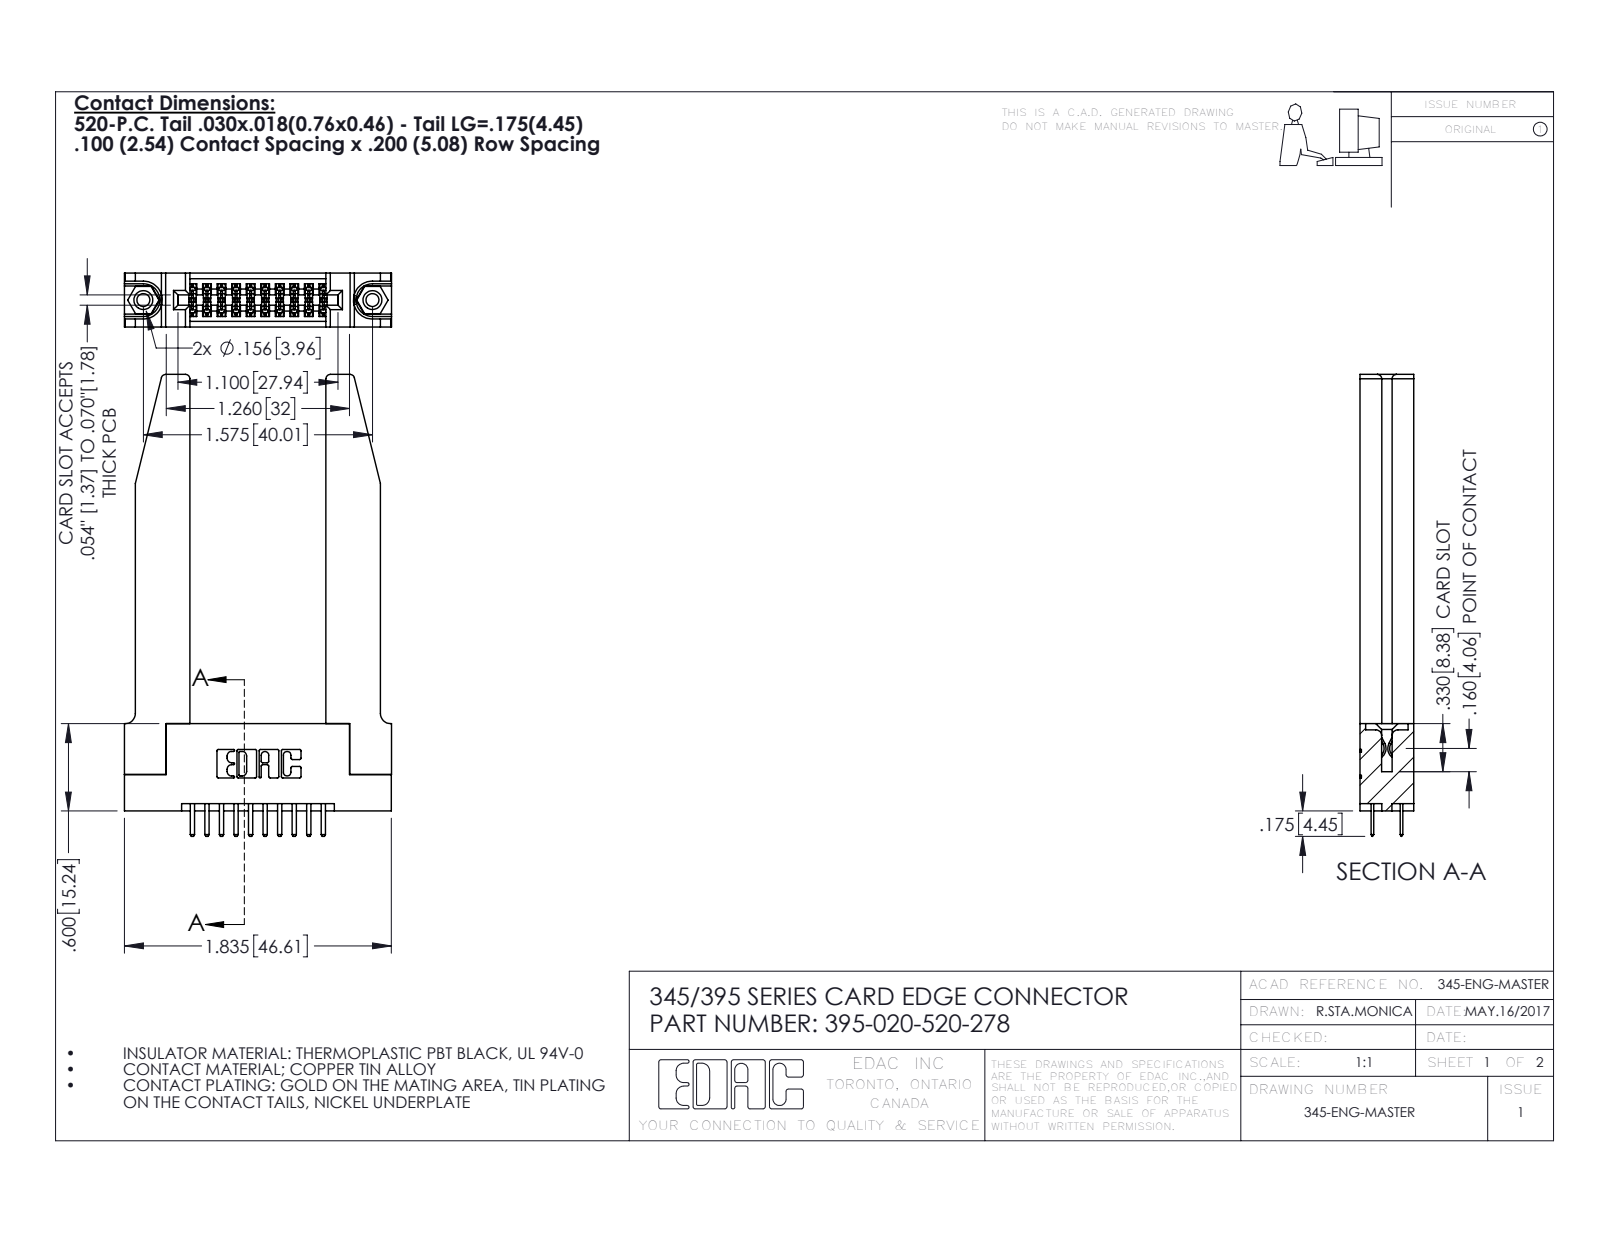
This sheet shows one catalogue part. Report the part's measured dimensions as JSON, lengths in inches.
{"part_name": "345-220-078_345-220-078; 345 Part_Flush Mounting Lugs - 0.156 Dia-TH; 345-292-001_345-293-120; 345-250-001_345-250-001-102 (+1 more)", "step_written_by": "SolidWorks 2016 (CONFIG_CONTROL_DESIGN)", "units": "inches", "bodies": {"solids": 25, "faces": 1440, "planar": 922, "cylindrical": 466, "other": 52}, "overall_size": [3.175, 1.836, 0.37], "volume_in3": 0.732, "surface_area_in2": 19.29, "round_holes": [[0.089, 2], [0.125, 2], [0.156, 2], [0.064, 1]], "round_bosses_or_shafts": [[0.155, 2]], "partial_cylinders_radius": [[0.006, 30], [0.01, 24], [0.01, 22], [0.03, 8], [0.007, 6], [0.031, 6], [0.026, 3], [0.014, 2]], "face_to_face_distances": [0.37, 0.072, 0.298, 0.2, 0.077, 0.15, 0.22, 0.148, 0.935, 0.225], "hole_center_spacings": [0.27, 1.344, 1.575]}
